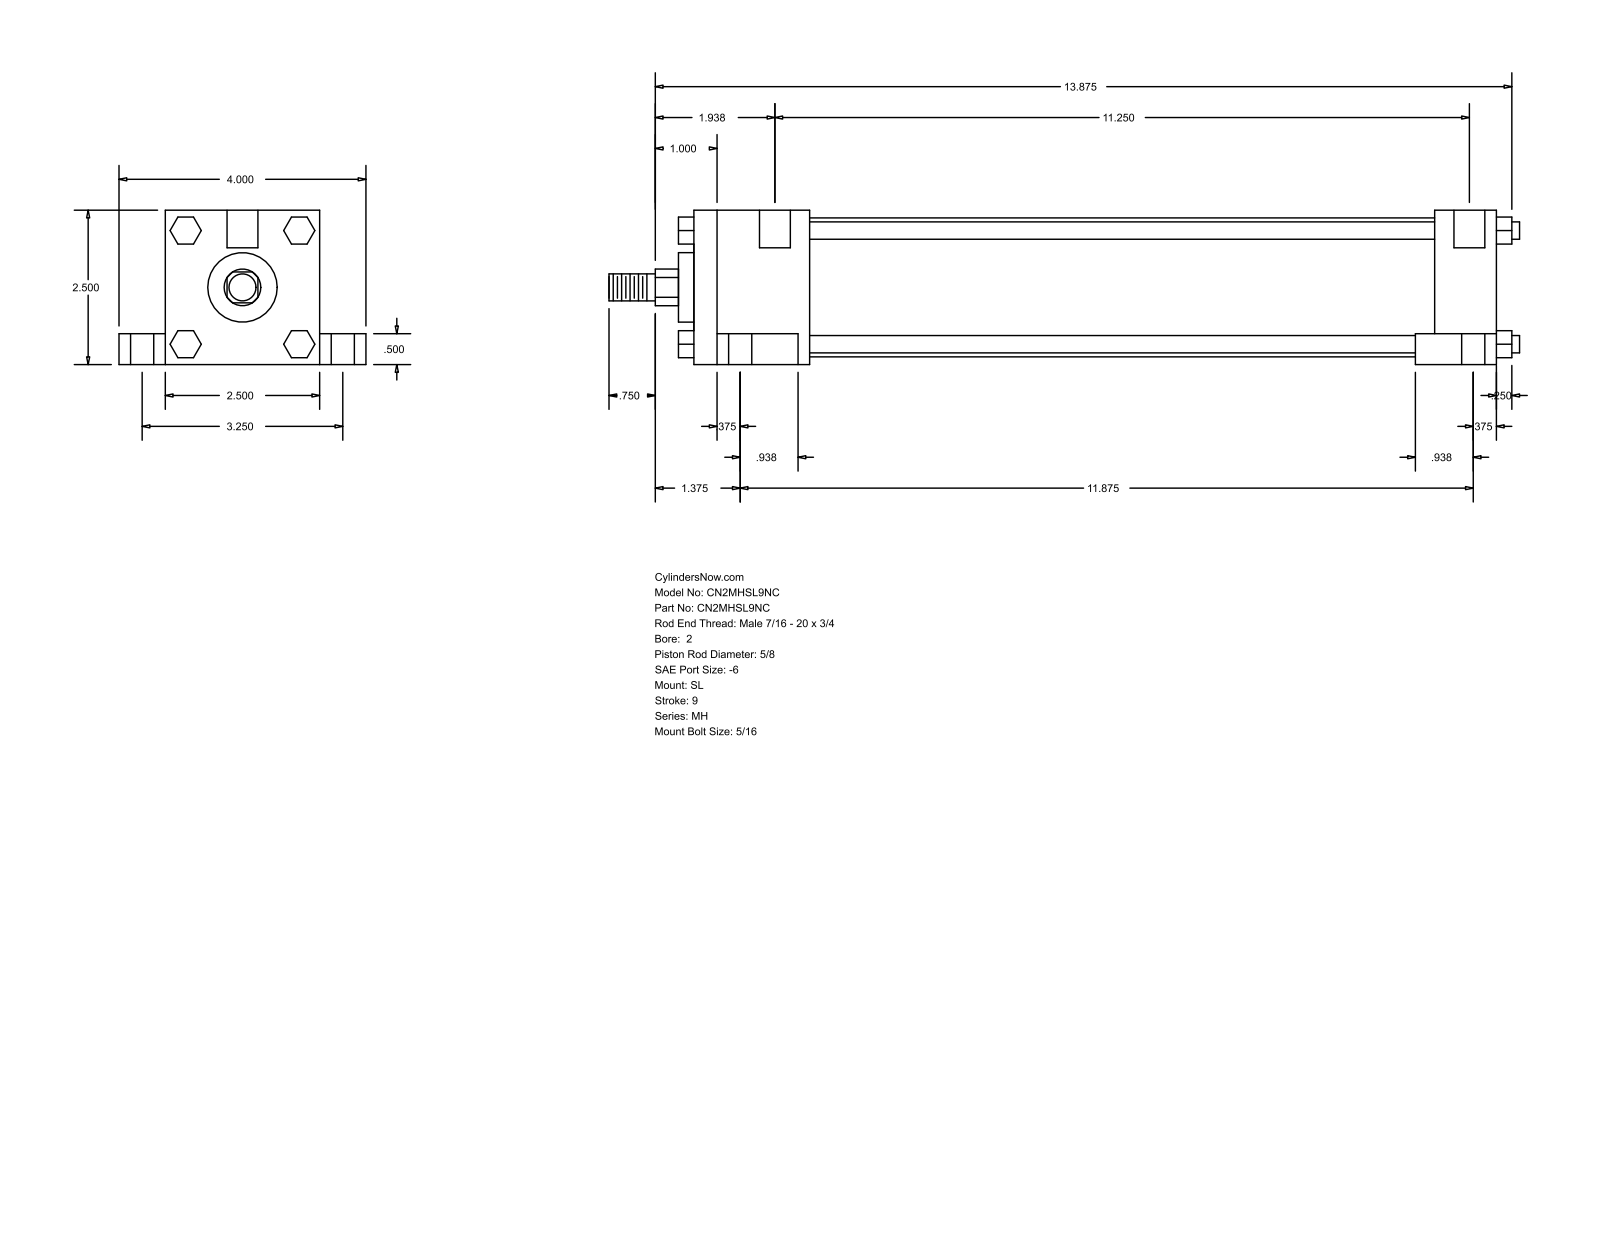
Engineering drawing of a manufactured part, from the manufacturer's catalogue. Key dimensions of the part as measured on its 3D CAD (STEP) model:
Part name (STEP PRODUCT): MH_SL__0200_0.625
STEP written by: GSSL Pune (CONFIG_CONTROL_DESIGN)
Units: millimetres
Bodies: 0 solids, 148 faces (112 planar, 36 cylindrical, 0 other)
Overall size (bounding box): 374.65 × 101.6 × 63.5
Round holes (diameter × count): ⌀5.56 ×4, ⌀9.53 ×4, ⌀15.88 ×4, ⌀12.7 ×2
Round bosses / shafts (diameter × count): ⌀7.14 ×4, ⌀57.15 ×1, ⌀28.57 ×1, ⌀15.88 ×1, ⌀11.11 ×1
Partial cylindrical surfaces — rounded edges, fillets, slot ends (radius × count): R7.54 ×1
Main face-to-face distances: 63.5, 330.19, 12.7, 19.05, 82.55, 50.8, 304.8, 25.39, 47.62, 257.18
Hole centre spacings: 41.3, 42.36, 43.67, 82.54, 290.29, 293.69, 295, 301.63
